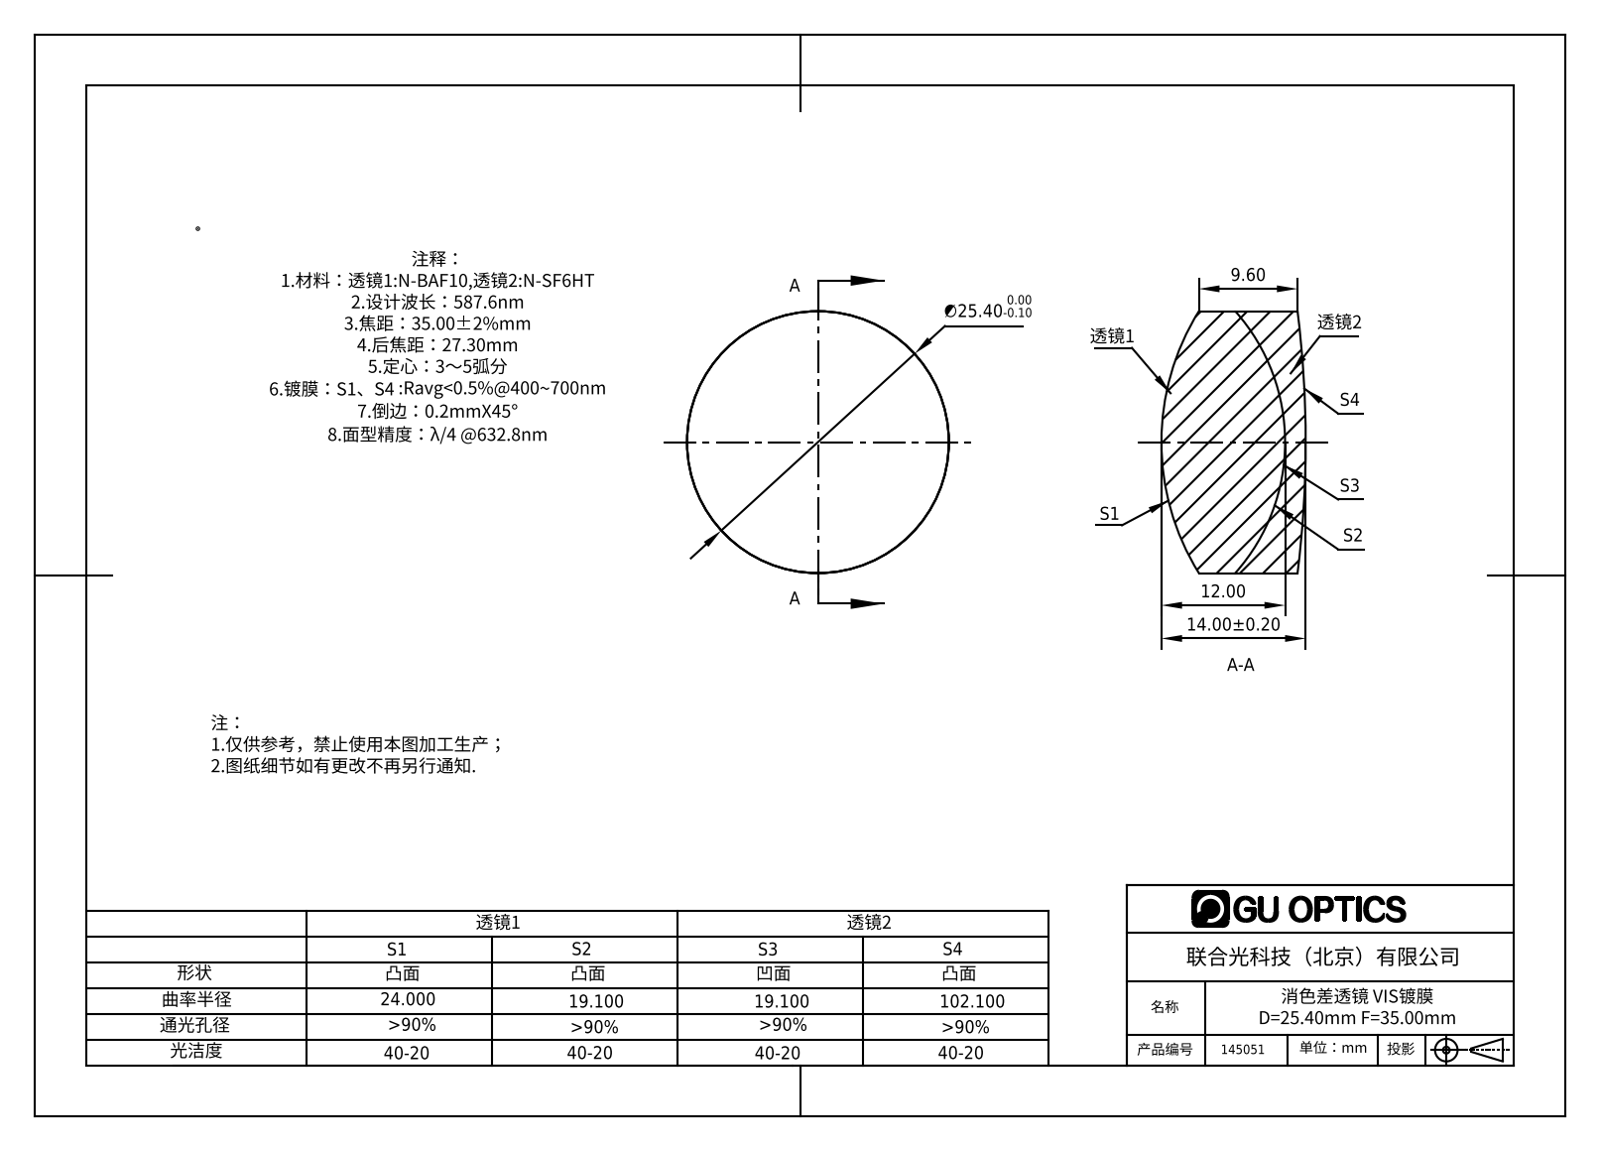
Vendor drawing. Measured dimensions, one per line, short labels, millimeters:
name: 145051
written by: SolidWorks 2016 (AUTOMOTIVE_DESIGN)
unit: mm
bodies: 2 solids, 12 faces (0 planar, 4 cylindrical, 8 other)
size: 25.4 × 25.4 × 14
volume: 5 997 mm³; area: 2 981 mm²
bosses: 1× ⌀25.4
